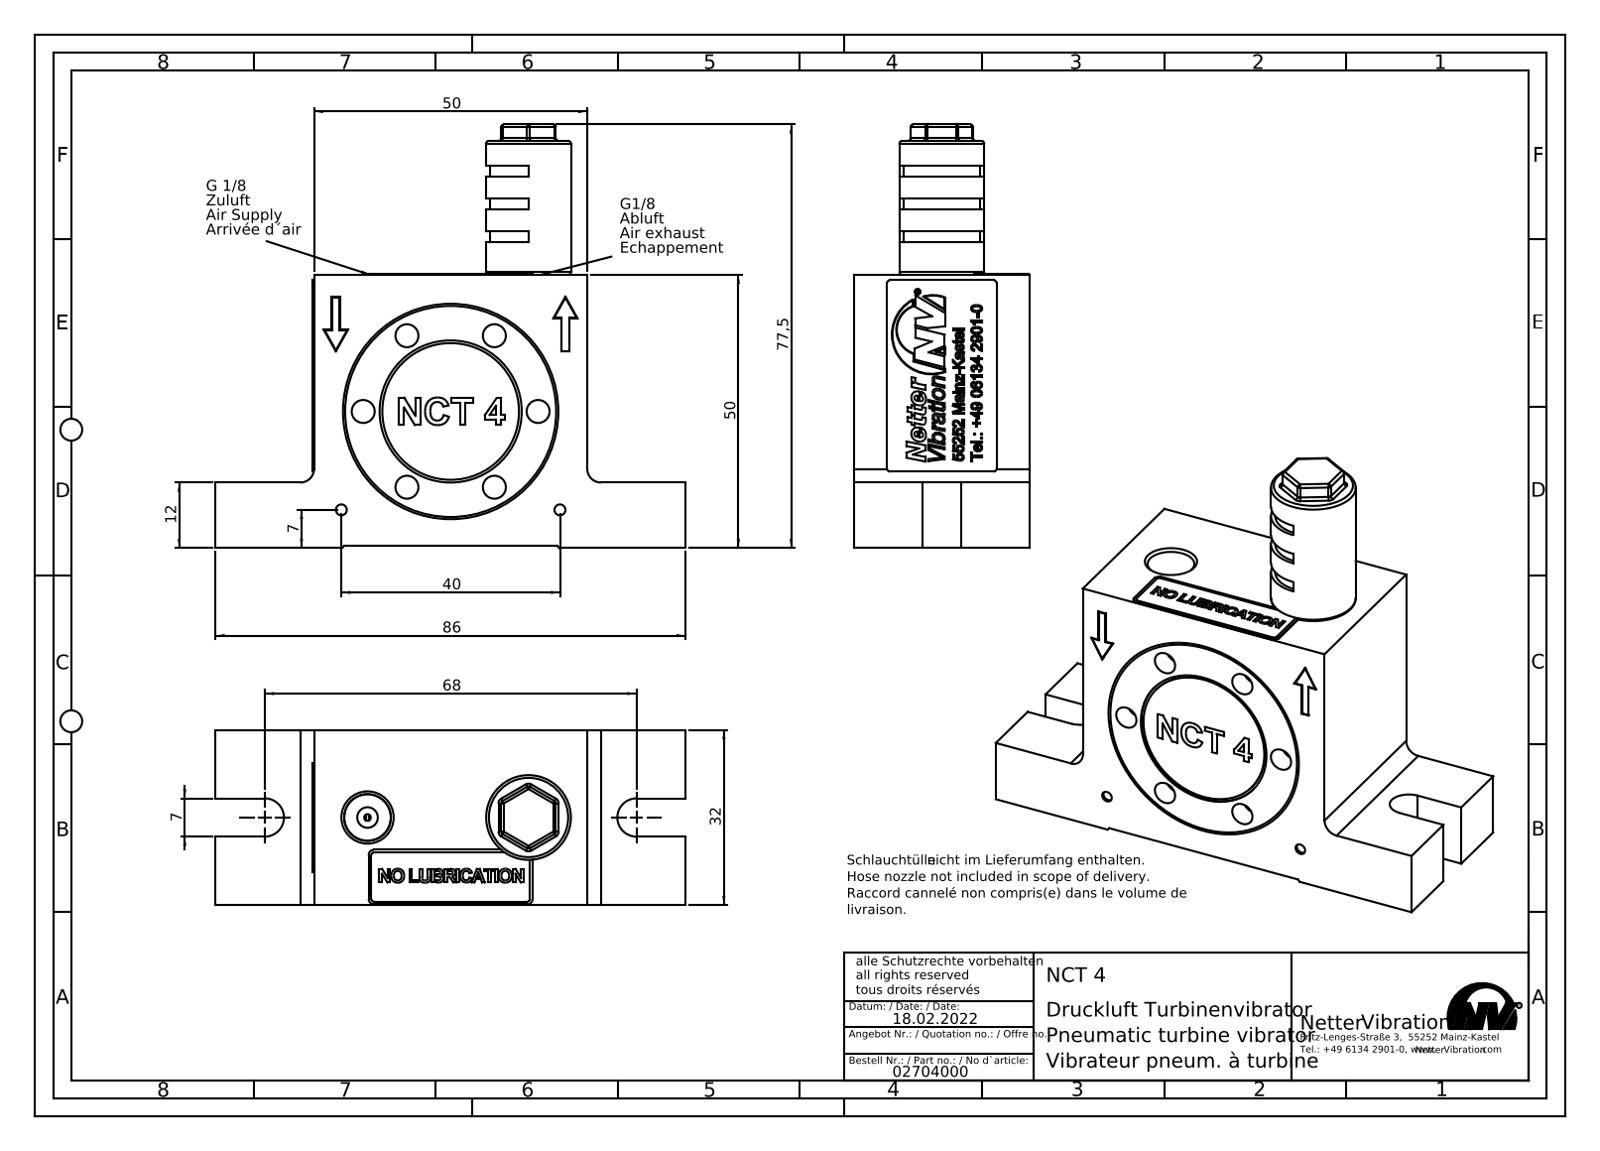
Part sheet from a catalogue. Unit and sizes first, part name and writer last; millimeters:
Units: millimetres
Overall size (bounding box): 86 × 77.5 × 32.25
Round holes (diameter × count): ⌀4.2 ×6, ⌀2 ×2, ⌀8.57 ×2, ⌀18 ×1, ⌀26 ×1, ⌀38.38 ×1
Round bosses / shafts (diameter × count): ⌀40 ×1, ⌀37.47 ×1, ⌀35.27 ×1, ⌀25 ×1, ⌀15.5 ×1, ⌀9.73 ×1
Partial cylindrical surfaces — rounded edges, fillets, slot ends (radius × count): R0.5 ×18, R2.5 ×2, R3.5 ×2, R7 ×1
Main face-to-face distances: 50, 32, 6, 0.4, 49.6, 8.25, 26, 23.75, 2.25, 31.95
Hole centre spacings: 16, 27.71, 12.69, 18.44, 26.91, 27.72, 28.3, 32.01
Volume: 96 237 mm³ · Surface area: 24 109 mm²
Bodies: 4 solids, 218 faces (90 planar, 69 cylindrical, 59 other)
Part name (STEP PRODUCT): NCT 4 Turbinenvibrator #02704000
STEP written by: SolidWorks 2015 (AUTOMOTIVE_DESIGN)
